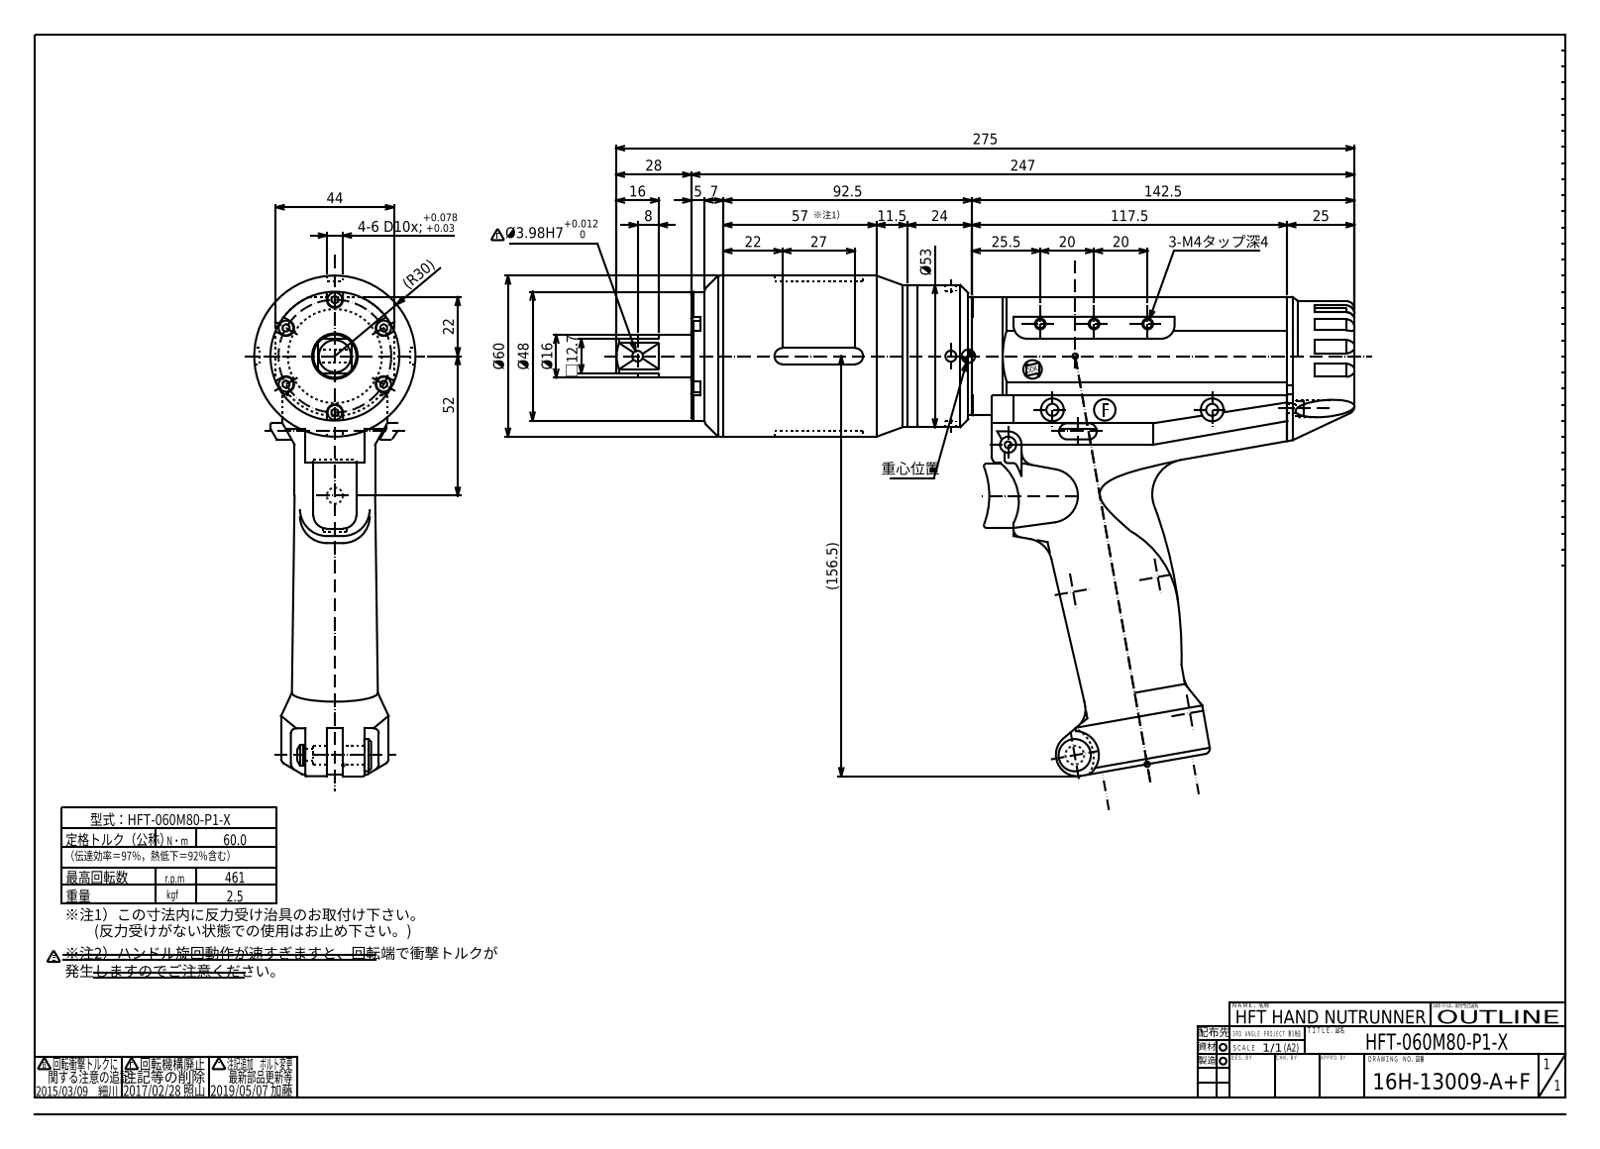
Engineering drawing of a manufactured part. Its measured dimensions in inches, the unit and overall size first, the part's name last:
Units: inches
Overall size (bounding box): 10.827 × 7.341 × 2.362
Round holes (diameter × count): ⌀0.134 ×13, ⌀0.097 ×11, ⌀0.165 ×5, ⌀0.128 ×4, ⌀0.161 ×4, ⌀0.228 ×4, ⌀0.236 ×4, ⌀0.177 ×3, ⌀0.276 ×3, ⌀0.181 ×2, ⌀0.335 ×2, ⌀0.063 ×1
Round bosses / shafts (diameter × count): ⌀0.039 ×24, ⌀0.217 ×9, ⌀0.118 ×9, ⌀0.098 ×5, ⌀0.114 ×4, ⌀0.063 ×4, ⌀0.157 ×3, ⌀1.181 ×2
Partial cylindrical surfaces — rounded edges, fillets, slot ends (radius × count): R0.02 ×18, R0.118 ×18, R0.098 ×8, R0.197 ×7, R0.079 ×6, R0.039 ×5, R0.048 ×5, R0.012 ×4
Main face-to-face distances: 0.236, 0.374, 0.138, 0.118, 1.496, 1.26, 0.984, 1.358, 1.122, 0.748
Hole centre spacings: 0.827, 0.216, 0.633, 1.007, 1.169, 1.312, 1.432, 1.528
Volume: 36.12 in³ · Surface area: 216.6 in²
Bodies: 6 solids, 1501 faces (700 planar, 375 cylindrical, 426 other)
Part name (STEP PRODUCT): HFT-060M80-P1-X(16H-13009+F)OUTLINE
STEP written by: Autodesk Inventor 2017 (AUTOMOTIVE_DESIGN)
